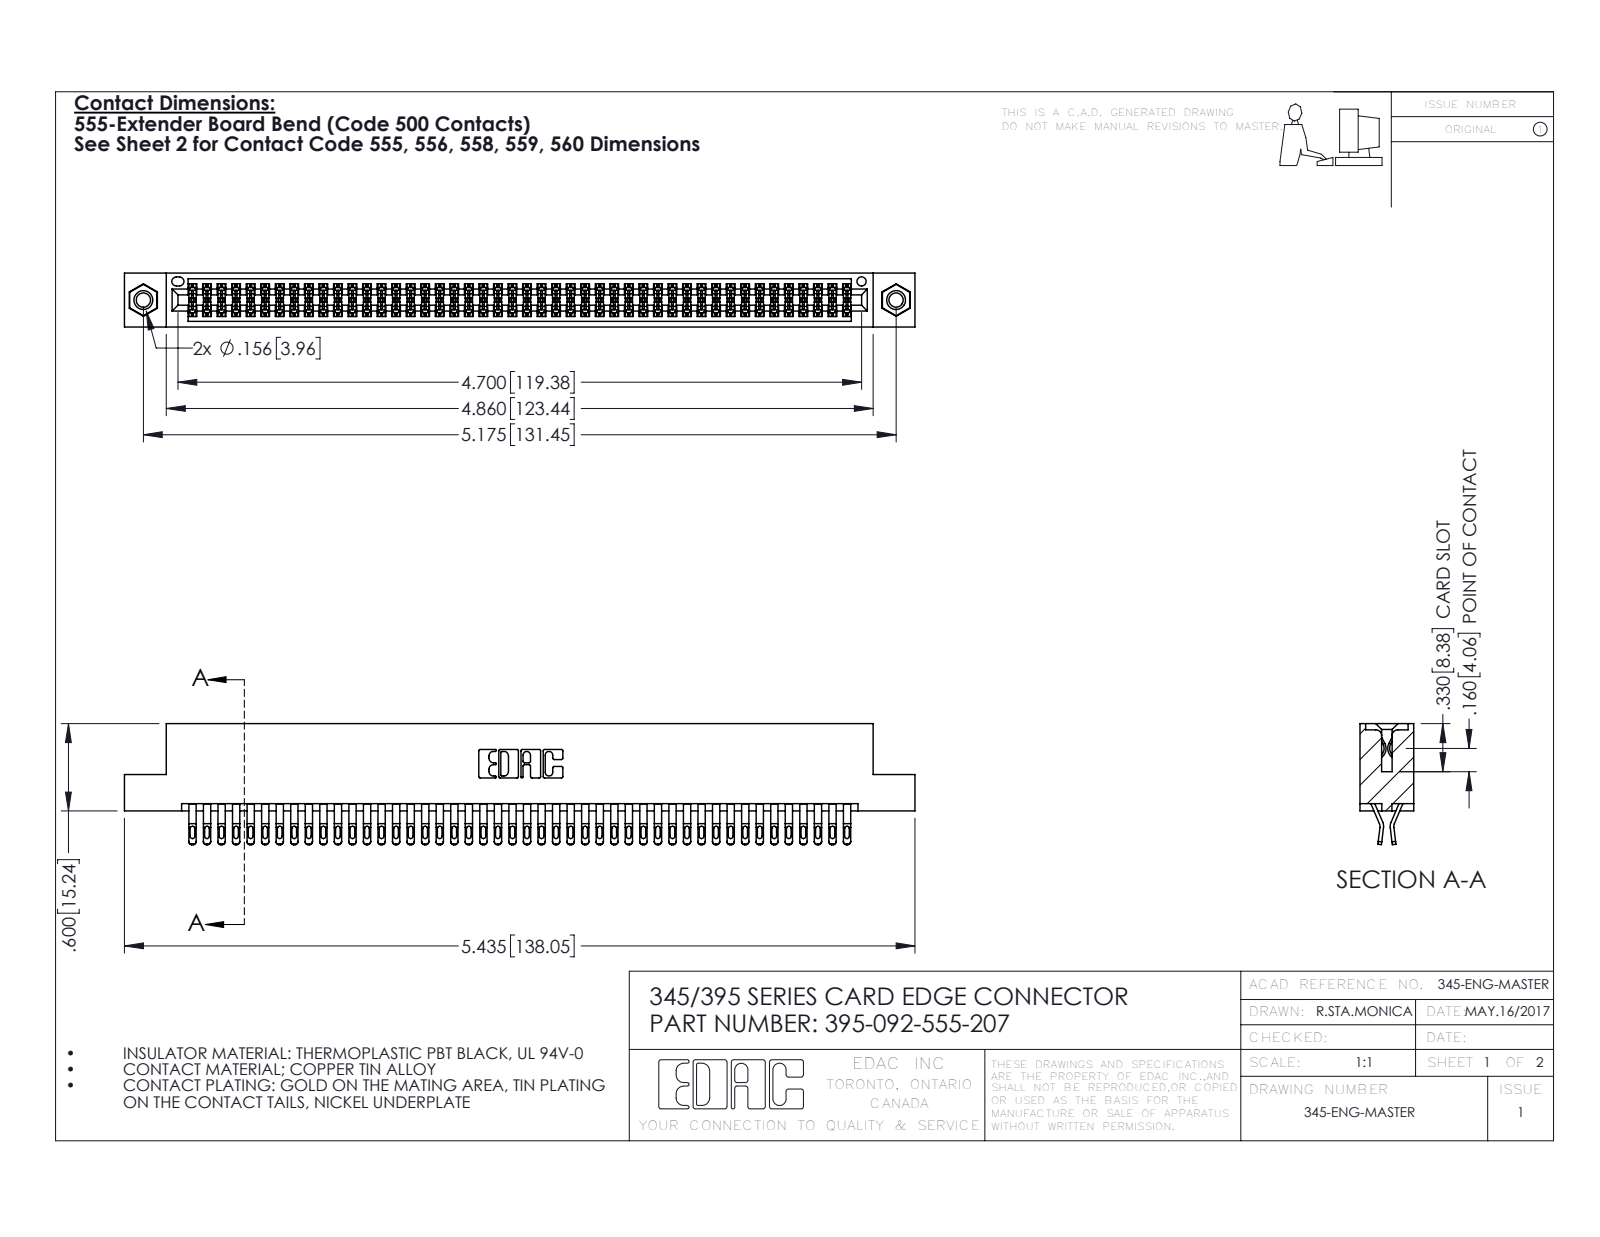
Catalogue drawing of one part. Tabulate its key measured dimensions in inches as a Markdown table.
| quantity | value |
| --- | --- |
| part name | 395-092-555-207; 345-250-001_345-250-005-103; 345 Part_Flush Mounting Lugs - 0.156 Dia-TI; 345-292-001_555 Tail |
| STEP written by | SolidWorks 2016 (CONFIG_CONTROL_DESIGN) |
| units | inches |
| bodies | 95 solids, 5338 faces (2964 planar, 2358 cylindrical, 16 other) |
| overall size | 5.435 × 0.832 × 0.37 |
| volume | 0.836 in³ |
| surface area | 32.99 in² |
| round holes (diameter × count) | 0.098 × 2, 0.125 × 2, 0.156 × 2, 0.064 × 1 |
| round bosses / shafts (diameter × count) | 0.155 × 2 |
| partial cylindrical surfaces (radius × count) | 0.016 × 230, 0.02 × 184, 0.006 × 138, 0.01 × 22, 0.007 × 6, 0.031 × 6, 0.026 × 3, 0.01 × 2 |
| main face-to-face distances | 0.072, 0.298, 0.025, 0.37, 0.2, 0.098, 0.272, 0.225, 0.175, 0.149 |
| hole center spacings | 0.27, 4.939, 5.175 |
